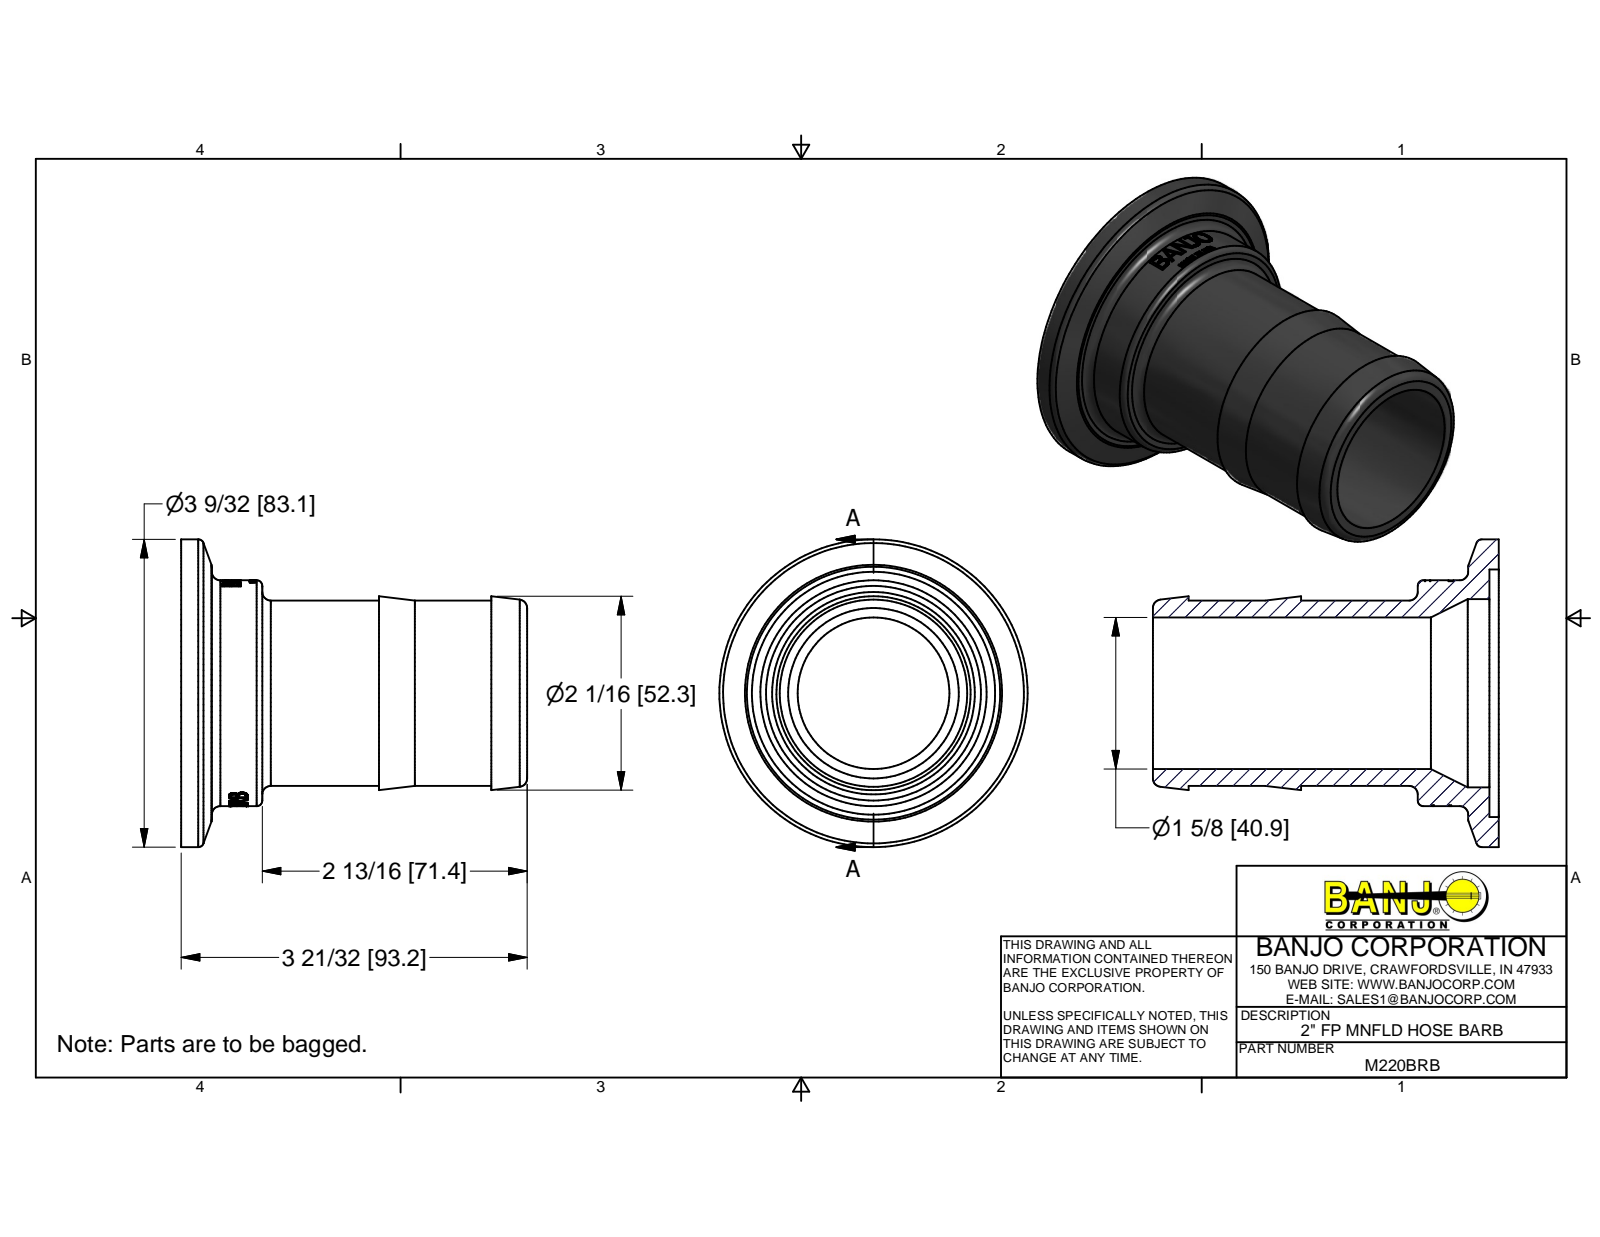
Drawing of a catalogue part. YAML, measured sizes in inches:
part_name: "M220BRB"
step_written_by: "Autodesk Inventor 2013 (AUTOMOTIVE_DESIGN)"
units: inches
bodies: {solids: 1, faces: 372, planar: 186, cylindrical: 42, other: 144}
overall_size: [3.67, 3.27, 3.27]
volume: 5.412
surface_area: 55.02
round_holes:
  - {diameter: 1.61, count: 1}
  - {diameter: 2, count: 1}
  - {diameter: 2.63, count: 1}
round_bosses_or_shafts:
  - {diameter: 3.27, count: 1}
  - {diameter: 2.4, count: 1}
  - {diameter: 1.97, count: 1}
partial_cylinders:
  - {radius: 1.19, count: 1}
face_to_face_distances: [0.1, 3.67, 3.57, 0.86, 0.76, 2.81, 0.324, 0.224, 0.535, 3.346]
